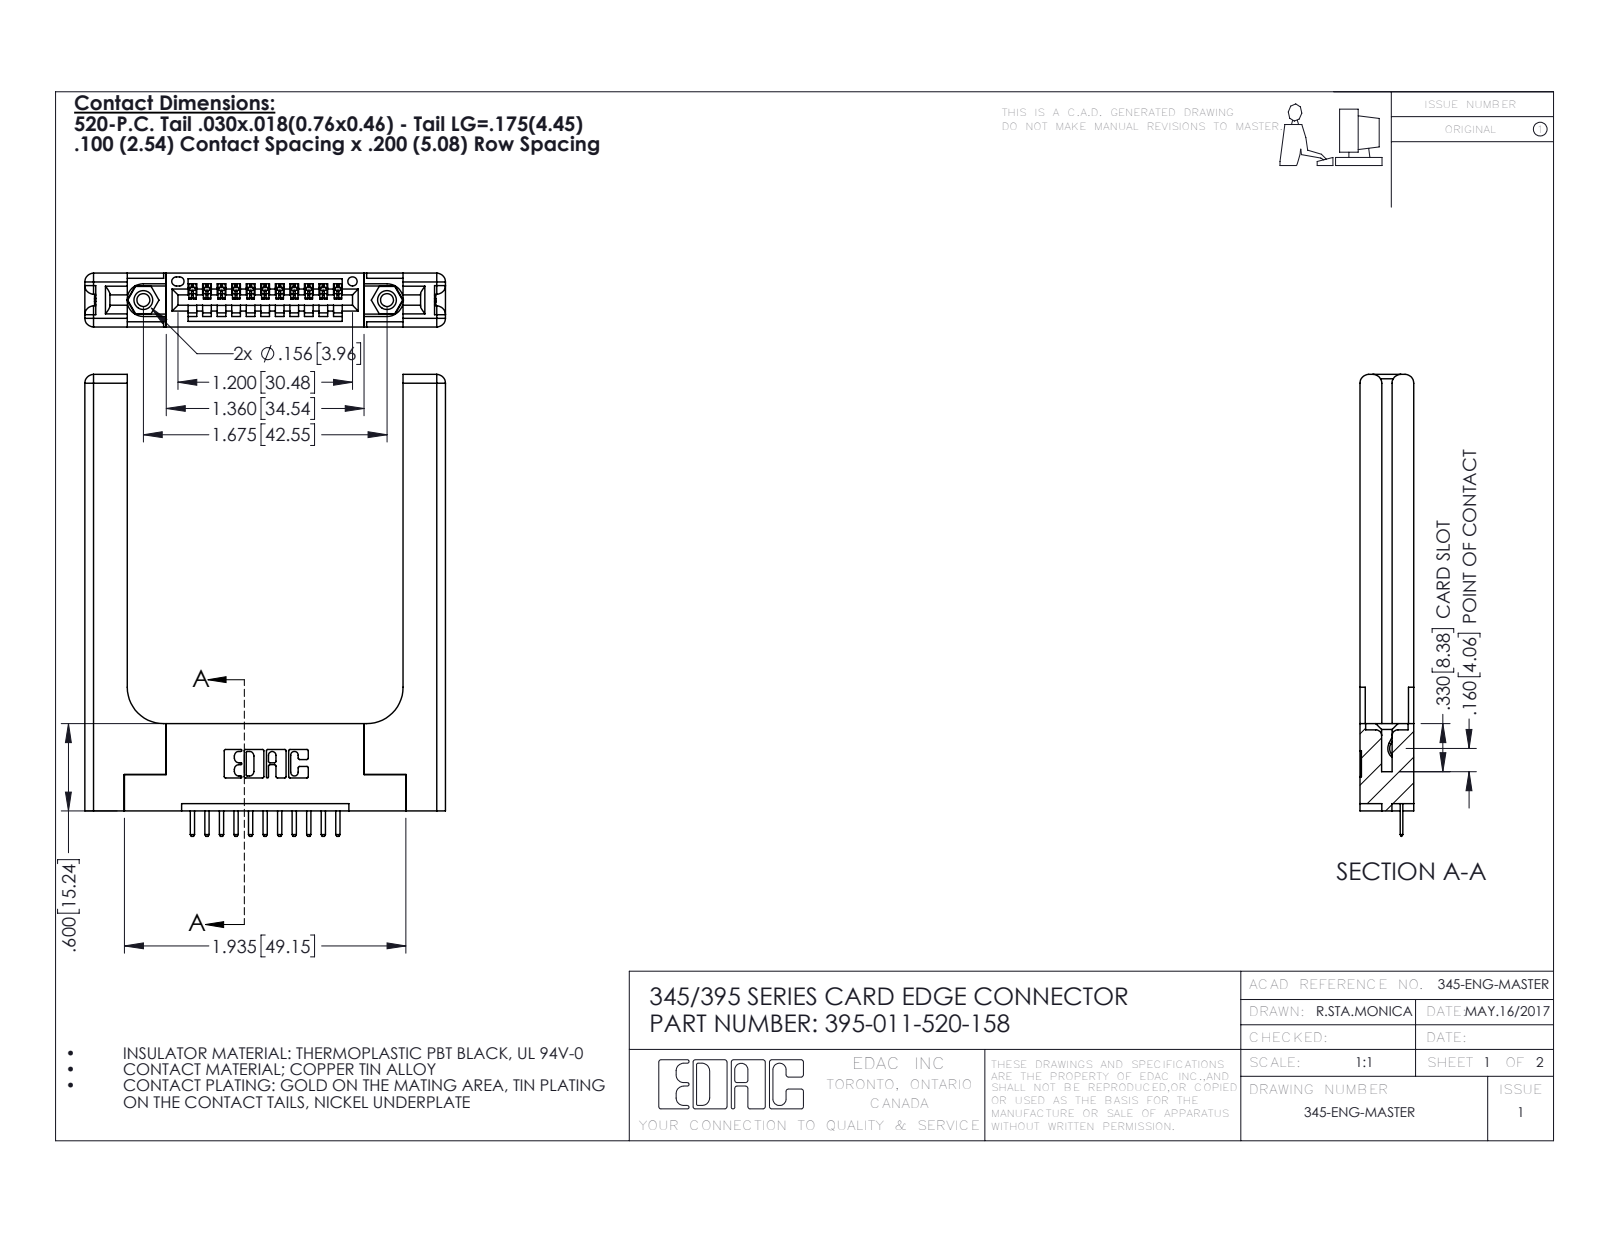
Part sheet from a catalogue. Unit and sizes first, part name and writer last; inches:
Units: inches
Overall size (bounding box): 3.175 × 2.479 × 0.37
Round holes (diameter × count): ⌀0.089 ×2, ⌀0.125 ×2, ⌀0.156 ×2, ⌀0.064 ×1
Round bosses / shafts (diameter × count): ⌀0.155 ×2
Partial cylindrical surfaces — rounded edges, fillets, slot ends (radius × count): R0.01 ×24, R0.006 ×22, R0.01 ×22, R0.06 ×16, R0.007 ×6, R0.031 ×6, R0.026 ×3, R0.03 ×2
Main face-to-face distances: 0.37, 0.15, 0.072, 0.22, 0.077, 0.148, 0.298, 0.2, 1.896, 0.071
Hole centre spacings: 0.27, 1.443, 1.675
Volume: 0.867 in³ · Surface area: 19.14 in²
Bodies: 16 solids, 1064 faces (690 planar, 314 cylindrical, 60 other)
Part name (STEP PRODUCT): 345-250-001_345-250-001-102; 345-292-001_345-293-120; 345 Part_Flush Mounting Lugs - 0.156 Dia-TH; 395-011-520-158 (+1 more)
STEP written by: SolidWorks 2016 (CONFIG_CONTROL_DESIGN)
